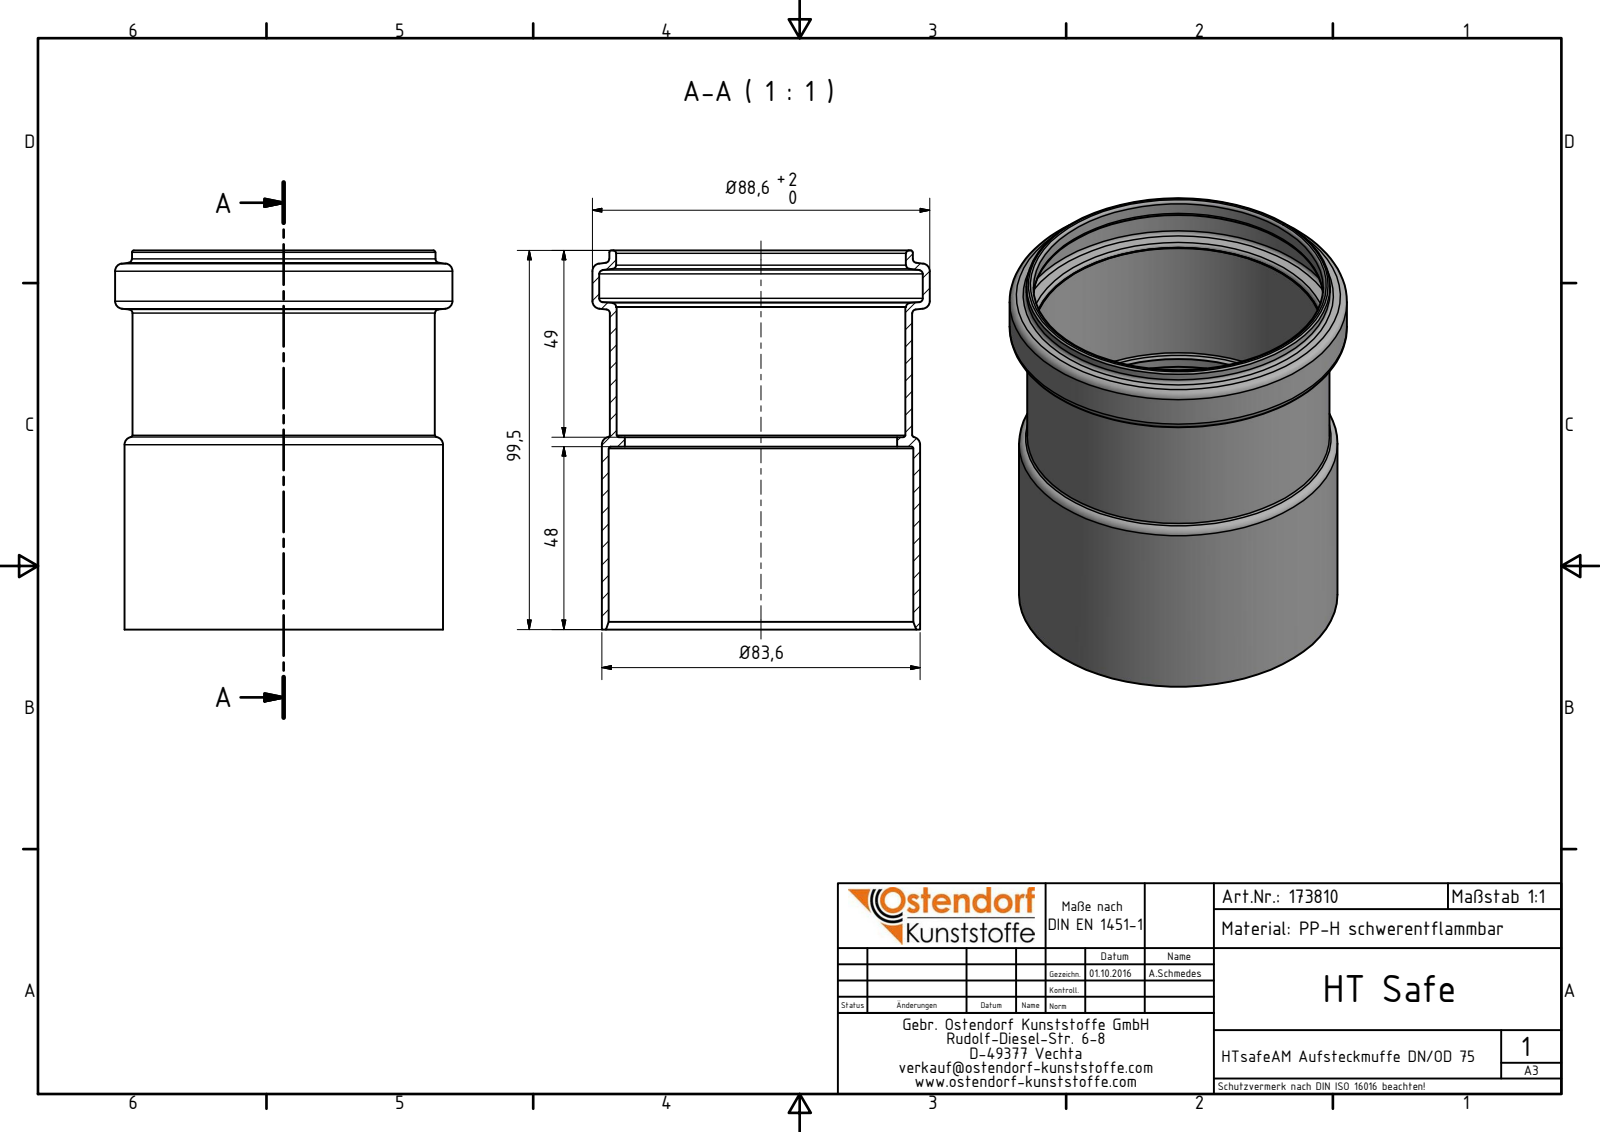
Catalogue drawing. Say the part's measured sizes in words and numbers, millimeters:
The part is named "173810 HTsafeAM DN_OD 75". Its 3-D file was written by "Autodesk Inventor 2016 (AUTOMOTIVE_DESIGN)". It is 1 solid with 34 faces: 5 planar, 10 cylindrical and 19 other. Overall it measures 99.5 by 88.6 by 88.6 millimeters. Its volume is 51 015 cubic millimeters and its surface area 56 008 square millimeters. Round holes: 1 of diameter 71.5, 1 of diameter 75.8, 1 of diameter 76.1, 1 of diameter 80, 1 of diameter 85. Round bosses or shafts: 1 of diameter 88.6, 1 of diameter 83.6, 1 of diameter 79.7, 1 of diameter 79.4. The main face-to-face distances are 2.5, 48, 50.5, 99.5, 51.5, 49, 84.62, 36.62, 34.12, 14.88.
